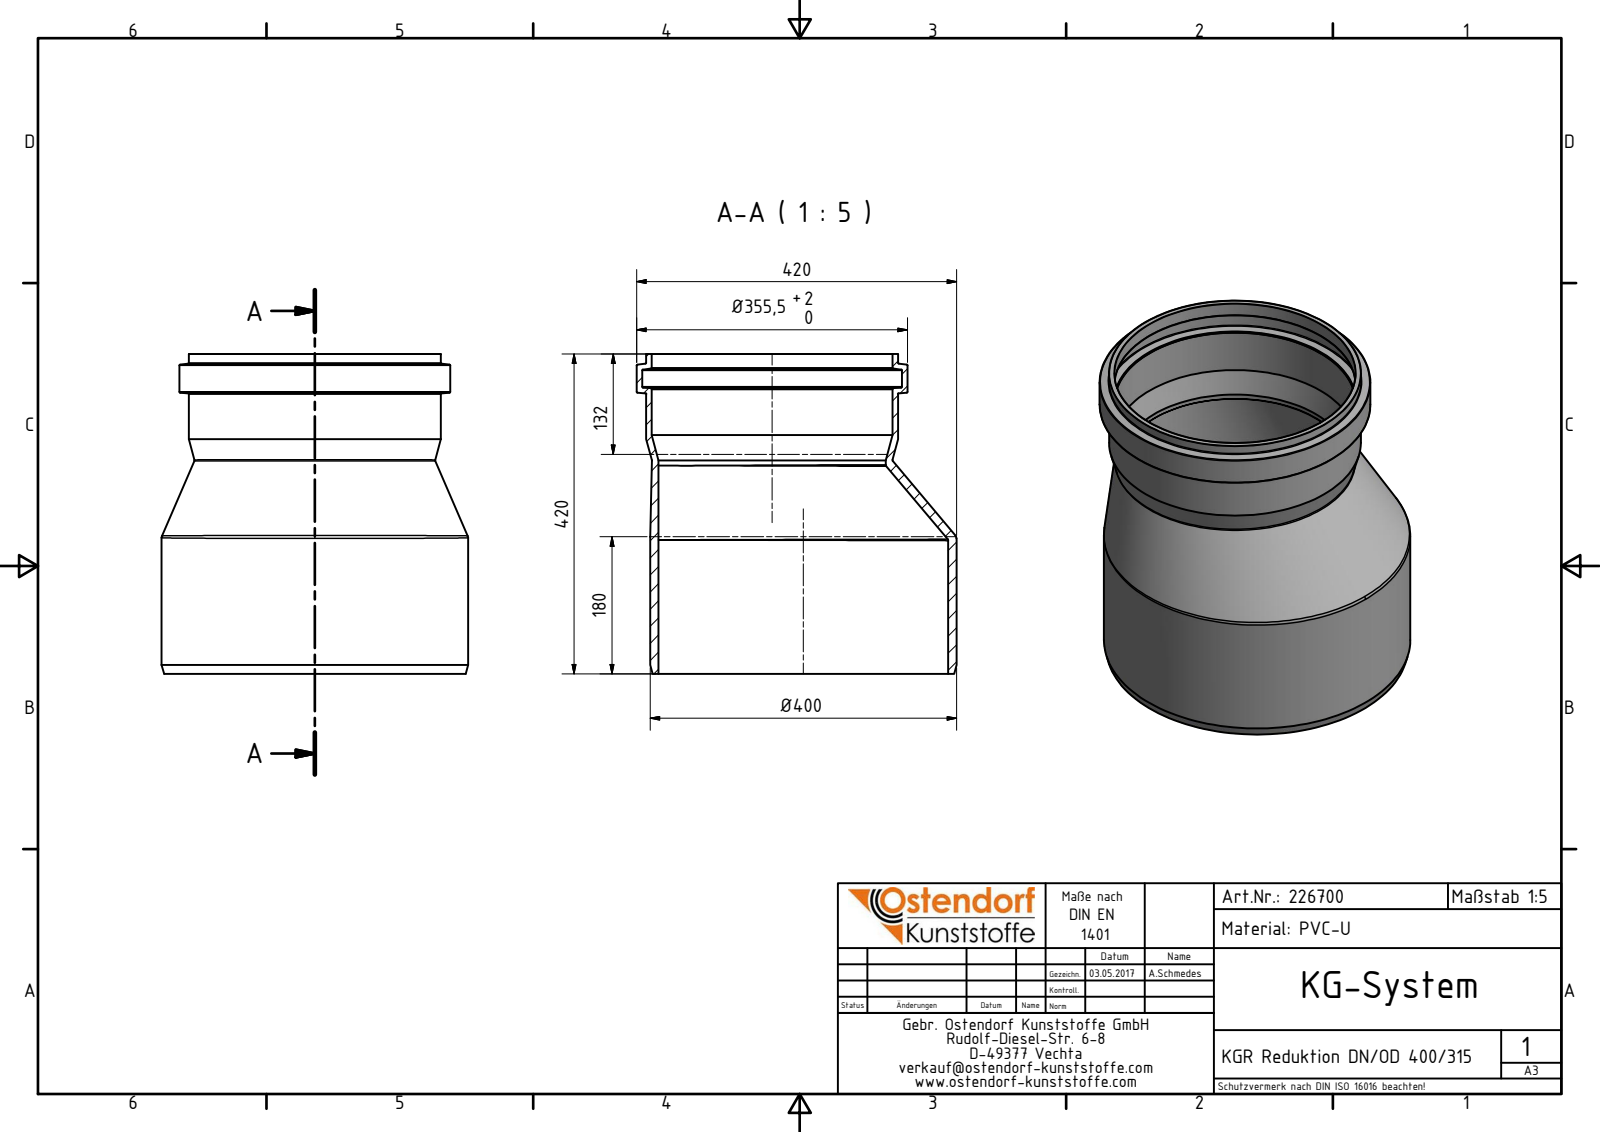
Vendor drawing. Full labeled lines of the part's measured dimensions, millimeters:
Part name (STEP PRODUCT): 226700 KGR Reduktion DN_OD 400_315
STEP written by: Autodesk Inventor 2016 (AUTOMOTIVE_DESIGN)
Units: millimetres
Bodies: 1 solid, 36 faces (3 planar, 10 cylindrical, 23 other)
Overall size (bounding box): 420 × 420 × 402.35
Volume: 4 993 000 mm³ · Surface area: 1 038 000 mm²
Round holes (diameter × count): ⌀298.2 ×1, ⌀316 ×1, ⌀316.3 ×1, ⌀340.9 ×1, ⌀380.35 ×1
Round bosses / shafts (diameter × count): ⌀402.35 ×1, ⌀355.5 ×1, ⌀330.9 ×1, ⌀330.6 ×1
Main face-to-face distances: 420, 373.45, 46.55
Hole centre spacings: 41.07
